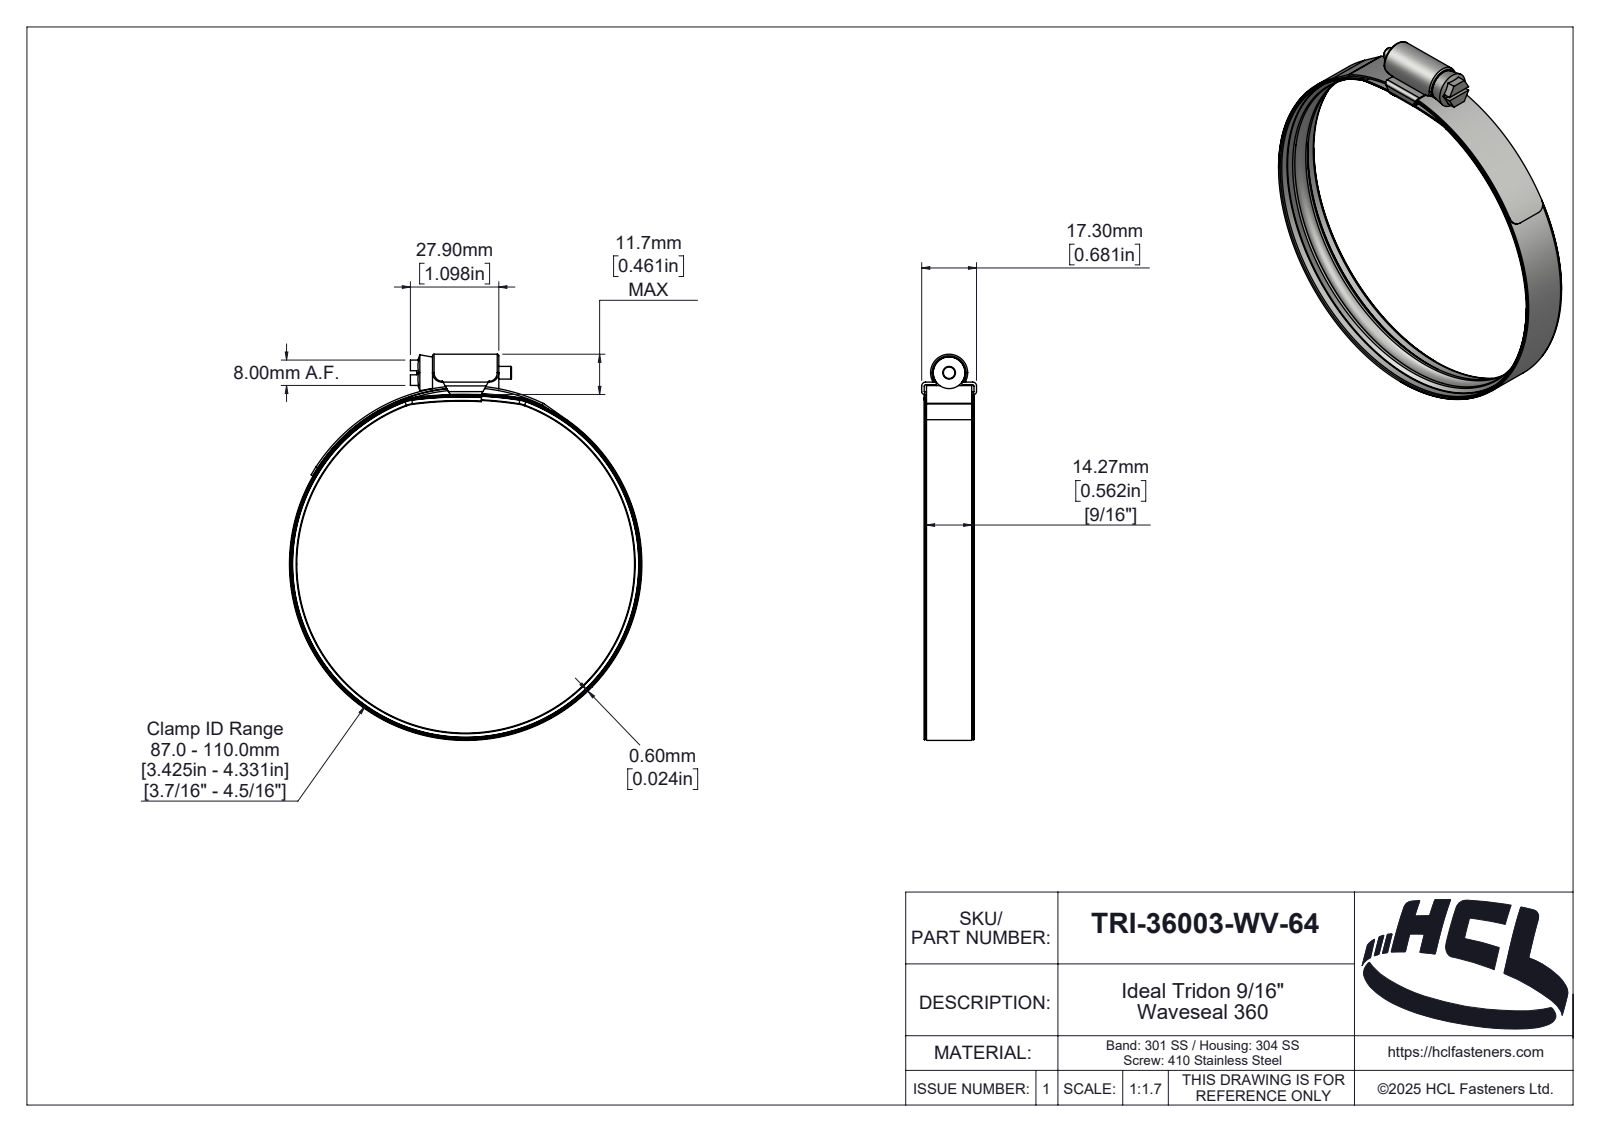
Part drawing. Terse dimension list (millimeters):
name: TRI-36003-WV-64
written by: SolidWorks 2025 (AUTOMOTIVE_DESIGN)
unit: mm
bodies: 4 solids, 418 faces (42 planar, 119 cylindrical, 257 other)
size: 121.8 × 111.2 × 17.3
volume: 7 566 mm³; area: 27 421 mm²
holes: 1× ⌀109.4, 1× ⌀110
bosses: 1× ⌀111.2, 1× ⌀109.8, 1× ⌀10, 1× ⌀4
rounds: 6× R0.5, 4× R3, 2× R0.1, 2× R0.9, 2× R1.2, 2× R9.9, 2× R10.1, 1× R0.46
face distances: 0.8, 14.26, 3.1, 0.6, 2.3, 3.9, 27.9, 1.52, 15.78, 16.5
